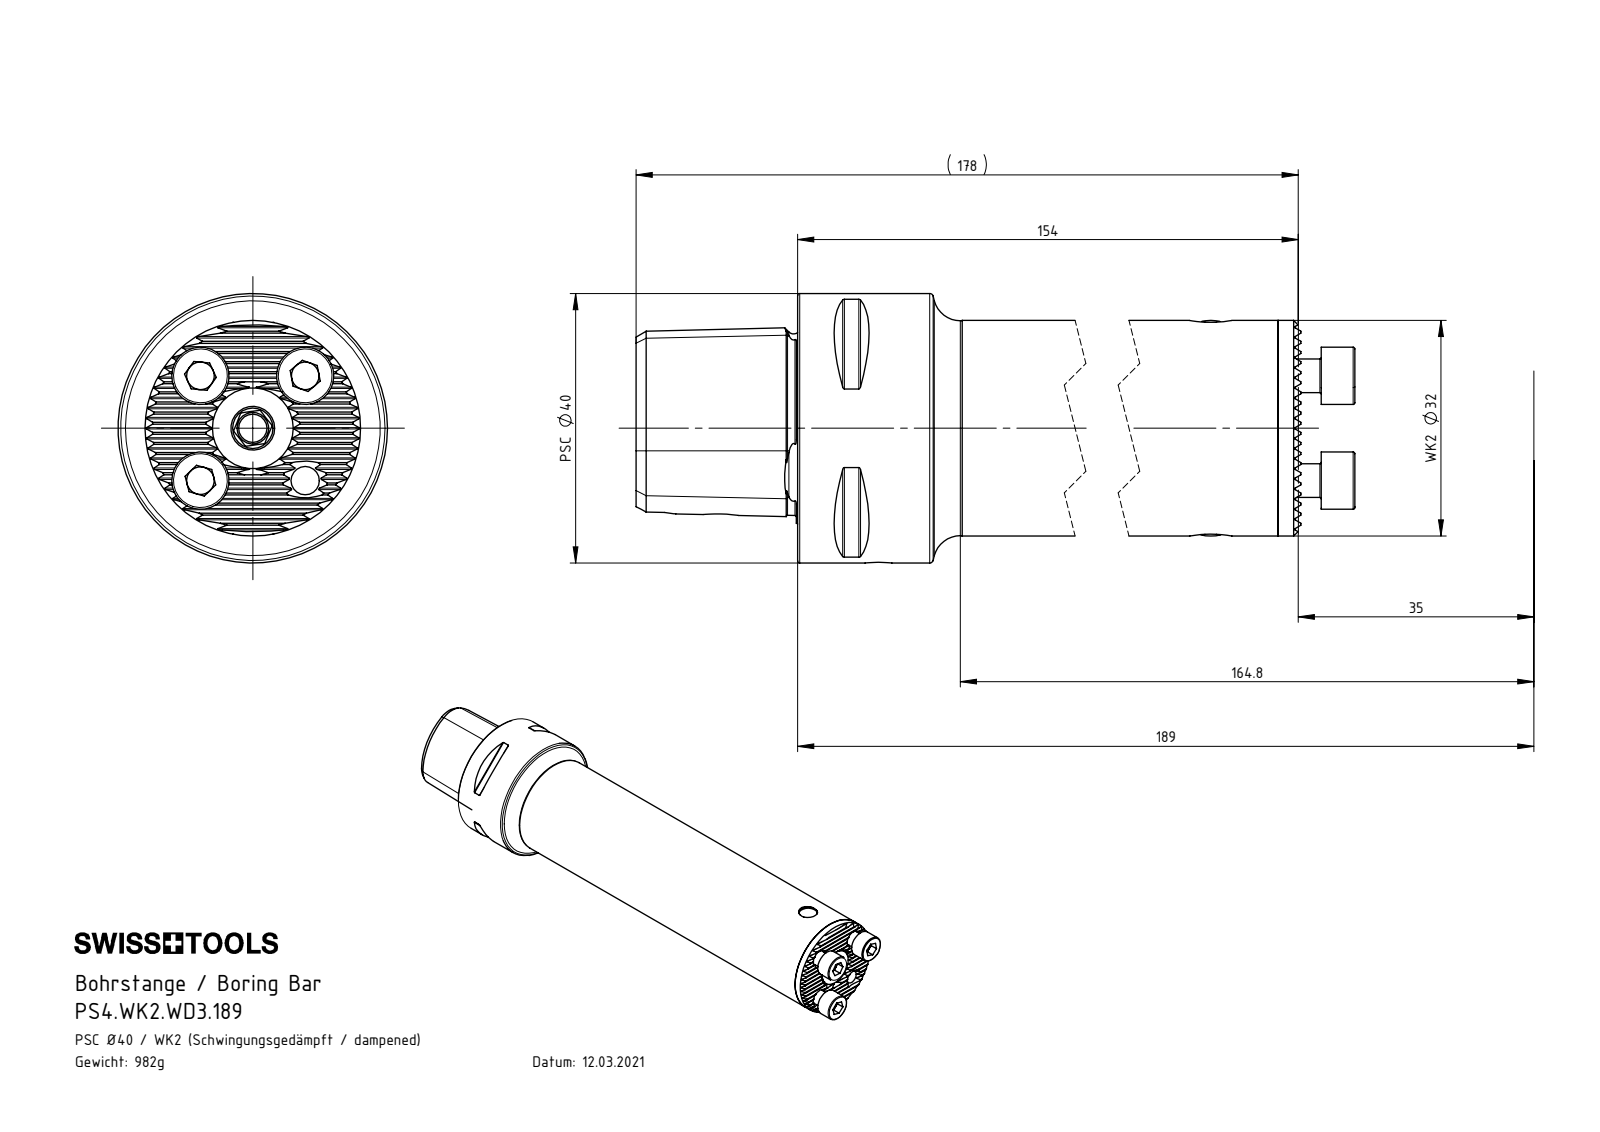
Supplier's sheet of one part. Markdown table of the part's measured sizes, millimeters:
| quantity | value |
| --- | --- |
| part name | WD3-ER1.011.082_A; WD3-ER1.026.087_A; DIN 3771 - 23x2; DIN 3771 - 13x4 (+8 more) |
| STEP written by | SolidWorks 2017 (AUTOMOTIVE_DESIGN) |
| units | millimeters |
| bodies | 16 solids, 499 faces (236 planar, 110 cylindrical, 153 other) |
| overall size | 186.4 × 40 × 40 |
| volume | 129 723 mm³ |
| surface area | 62 101 mm² |
| round holes (diameter × count) | 4.2 × 5, 6 × 2, 4 × 1, 4.6 × 1, 6.8 × 1, 7 × 1, 7.4 × 1, 8.2 × 1, 8.5 × 1, 10.2 × 1, 12 × 1, 12.5 × 1 |
| round bosses / shafts (diameter × count) | 8.5 × 3, 5 × 3, 40 × 1, 32 × 1, 27 × 1, 26.7 × 1, 26 × 1, 23.8 × 1 |
| partial cylindrical surfaces (radius × count) | 0.12 × 21, 0.3 × 8, 3 × 1 |
| main face-to-face distances | 6, 93.4, 2.6, 1.3, 134, 3.9, 3.2, 33.75, 133.15, 99.4 |
| hole center spacings | 11, 15.56, 22.01, 23.5, 129, 152.5 |
